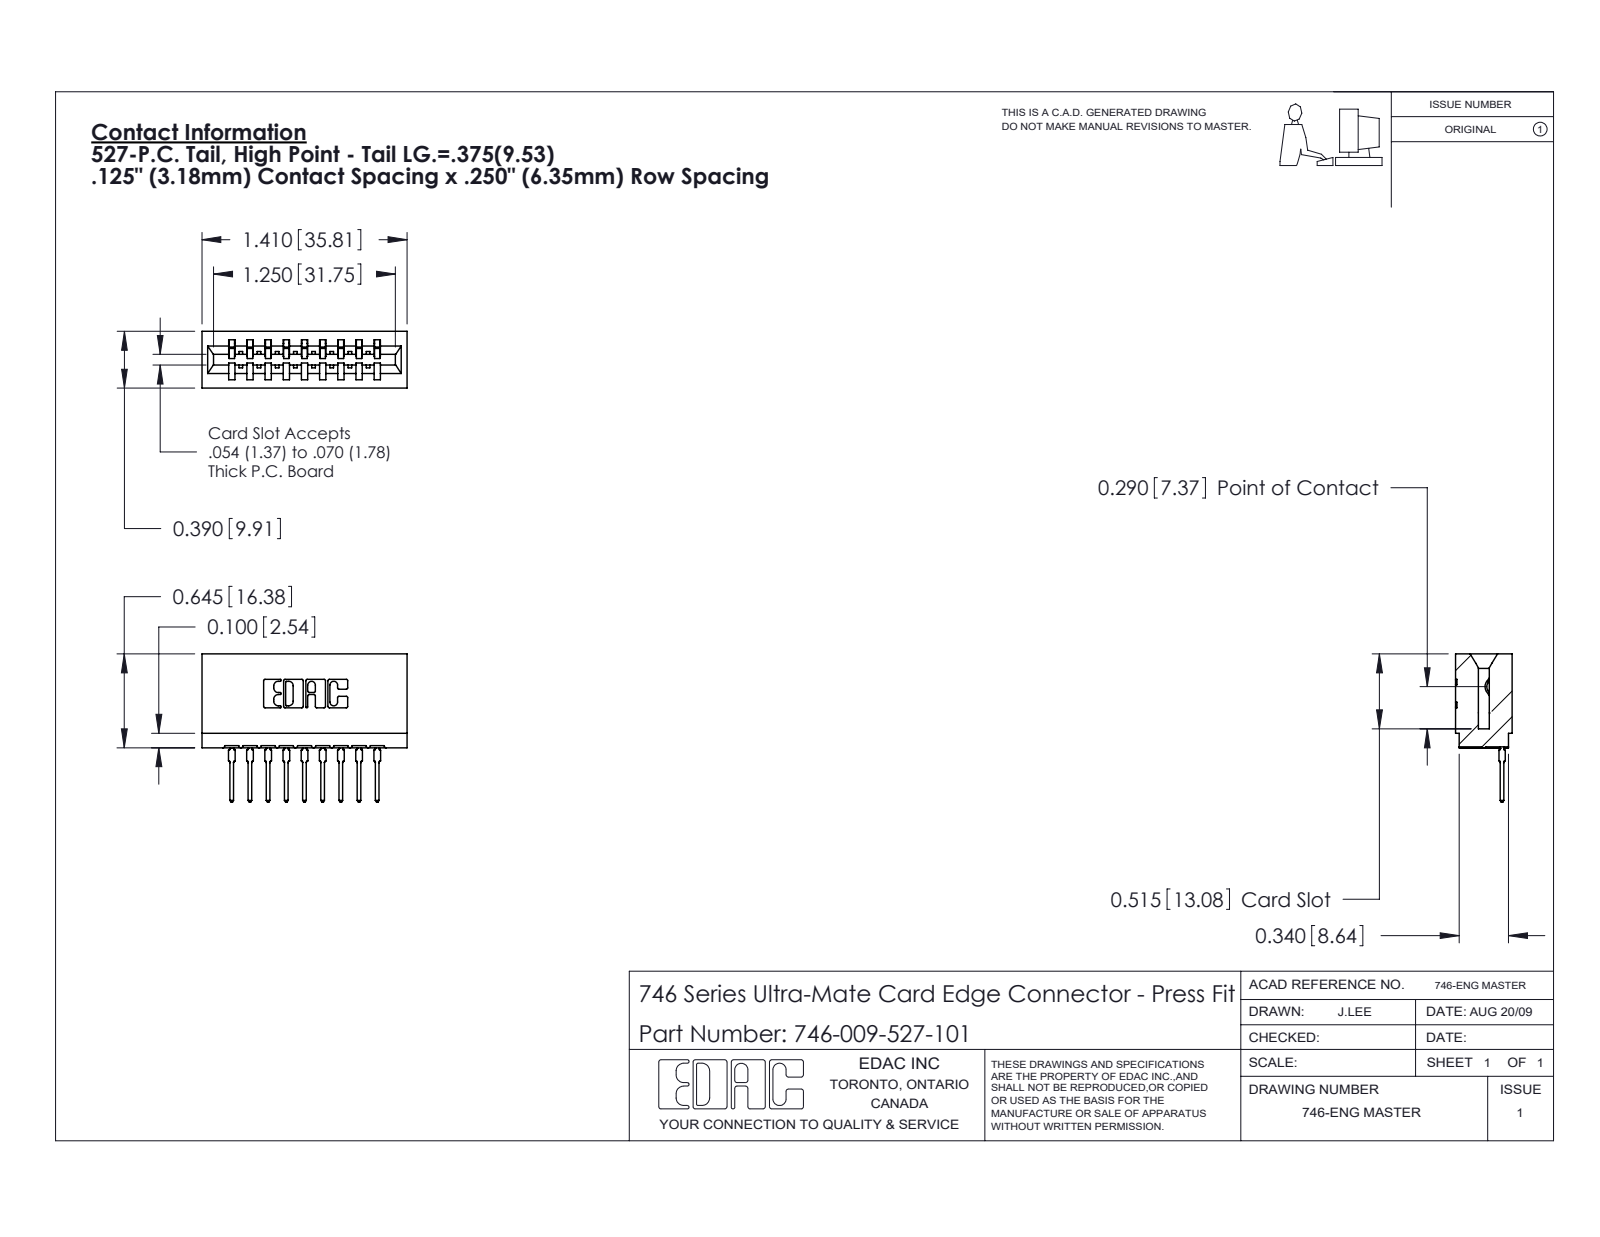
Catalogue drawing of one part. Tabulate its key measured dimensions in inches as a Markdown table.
| quantity | value |
| --- | --- |
| part name | 746-292-001_527; 746-009-527-101; 746 Part_.515 Slot Depth - 01 |
| STEP written by | SolidWorks 2020 (CONFIG_CONTROL_DESIGN) |
| units | inches |
| bodies | 10 solids, 1069 faces (622 planar, 213 cylindrical, 234 other) |
| overall size | 1.41 × 1.019 × 0.39 |
| volume | 0.243 in³ |
| surface area | 8.354 in² |
| partial cylindrical surfaces (radius × count) | 0.01 × 22, 0.021 × 18, 0.015 × 10, 0.007 × 6, 0.031 × 6, 0.005 × 4, 0.011 × 4, 0.026 × 3 |
| main face-to-face distances | 0.25, 0.5, 0.042, 0.333, 0.125, 0.125, 0.057, 0.292, 0.208, 0.375 |
